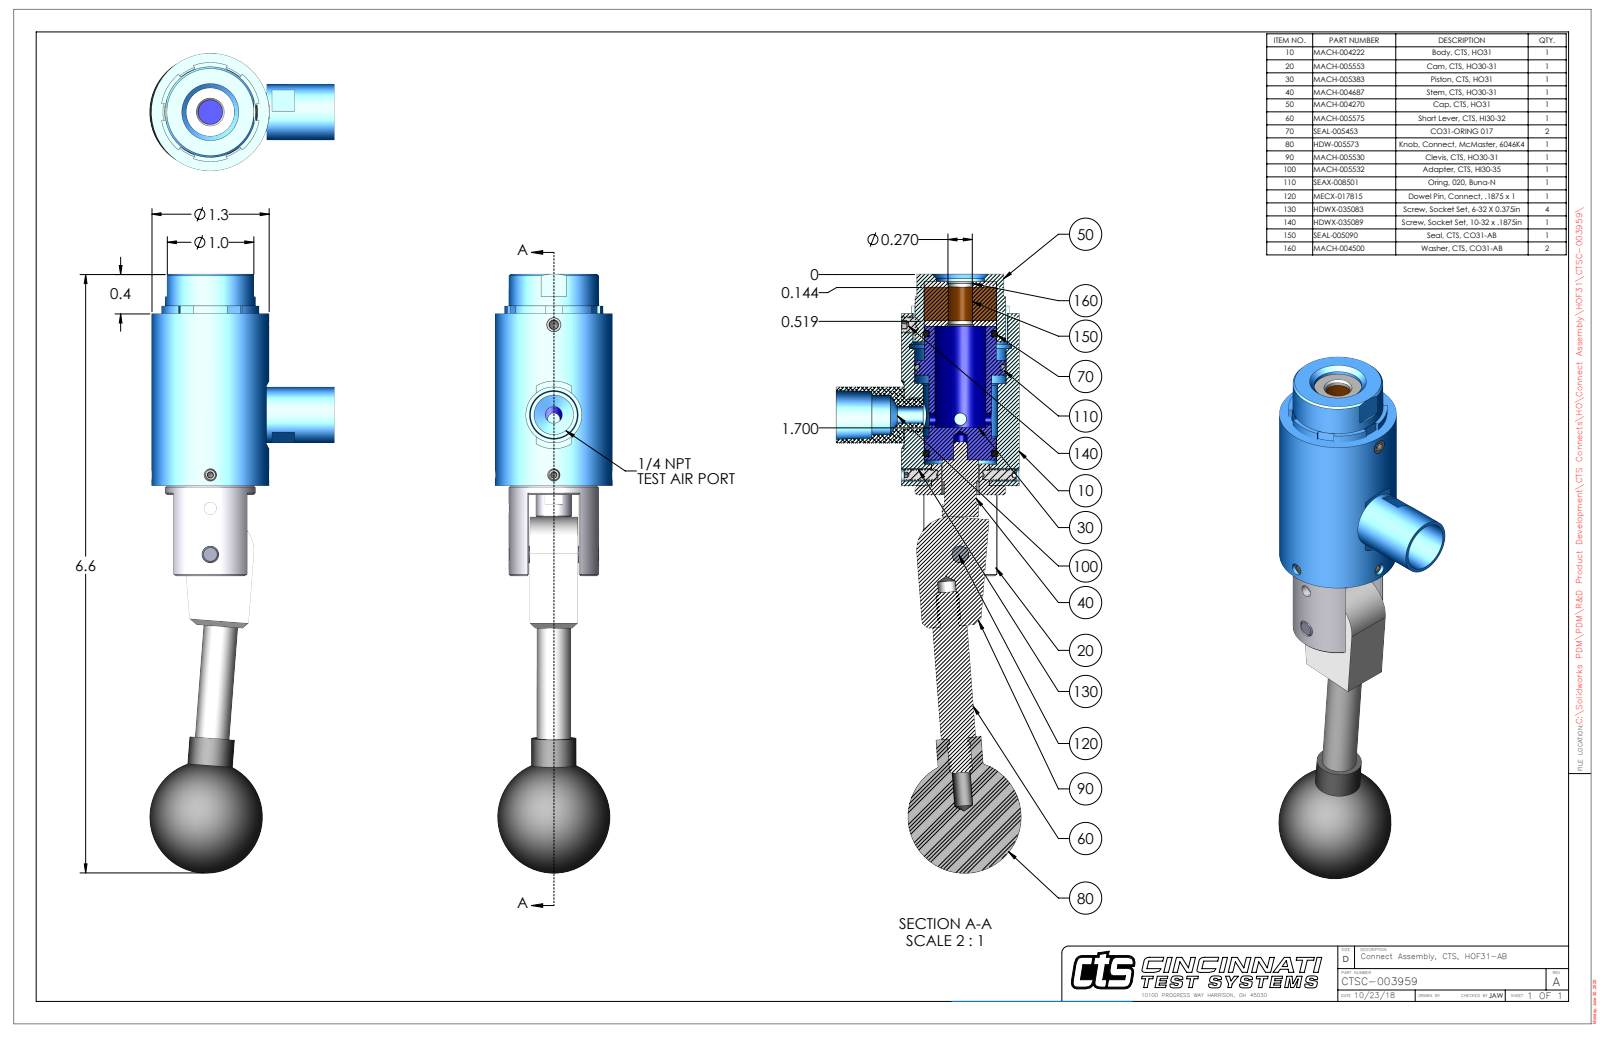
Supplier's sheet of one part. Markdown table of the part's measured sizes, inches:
| quantity | value |
| --- | --- |
| part name | CTSC-003959 |
| STEP written by | SolidWorks 2023 (AUTOMOTIVE_DESIGN) |
| units | inches |
| bodies | 14 solids, 532 faces (173 planar, 217 cylindrical, 142 other) |
| overall size | 6.636 × 2.042 × 1.3 |
| volume | 4.552 in³ |
| surface area | 46.83 in² |
| round holes (diameter × count) | 0.136 × 2, 0.201 × 2, 0.138 × 1, 0.15 × 1, 0.159 × 1, 0.187 × 1, 0.189 × 1, 0.19 × 1, 0.27 × 1, 0.272 × 1, 0.332 × 1, 0.418 × 1 |
| round bosses / shafts (diameter × count) | 0.138 × 2, 1.3 × 1, 1 × 1, 0.792 × 1, 0.79 × 1, 0.69 × 1, 0.63 × 1, 0.62 × 1 |
| partial cylindrical surfaces (radius × count) | 0.374 × 1, 0.375 × 1, 0.524 × 1, 0.547 × 1 |
| main face-to-face distances | 0.012, 0.542, 0.059, 0.434, 0.375, 0.53, 0.554, 0.493, 1.766, 1.825 |
| hole center spacings | 0.047, 0.51, 0.987, 0.997, 1.044, 1.497 |
